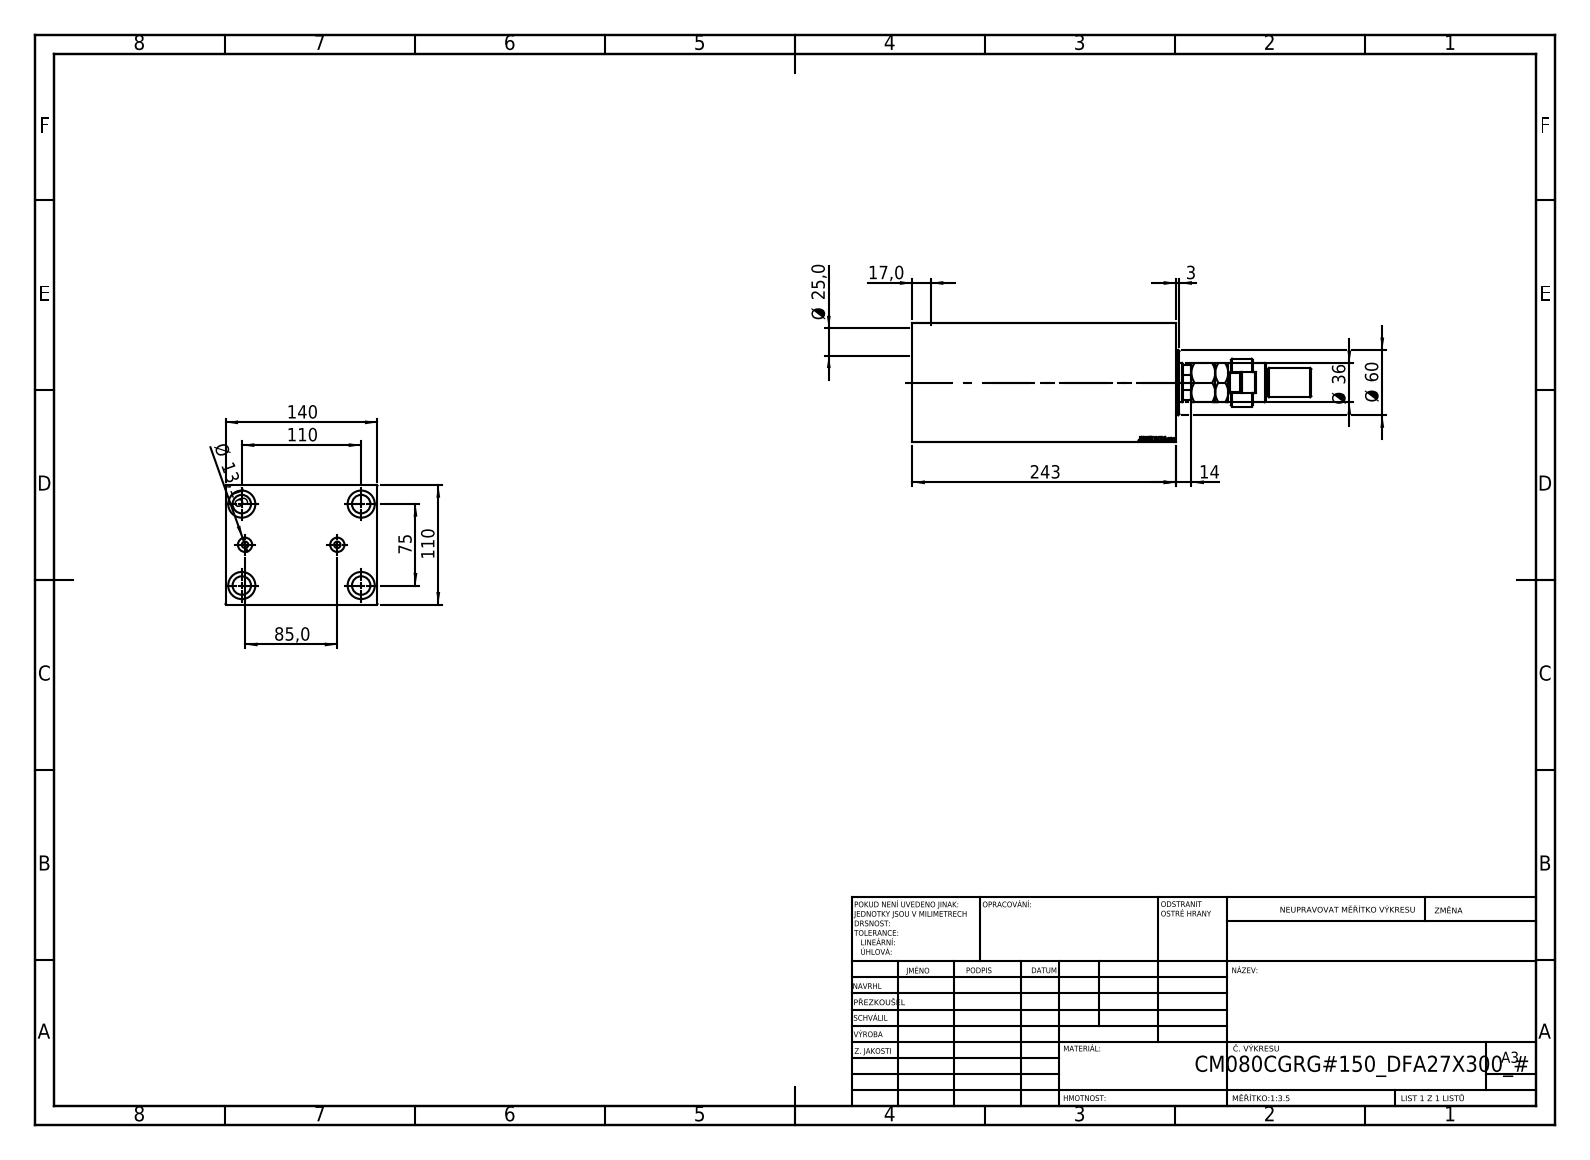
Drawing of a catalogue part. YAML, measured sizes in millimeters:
part_name: "V450CM_VC_B; V450CM_C_VCP; FEMALE_PART_FOR_DFA; V450CM_C_Body (+1 more)"
step_written_by: "SolidWorks 2019 (CONFIG_CONTROL_DESIGN)"
units: millimeters
bodies: {solids: 5, faces: 945, planar: 436, cylindrical: 71, other: 438}
overall_size: [367.5, 140, 110]
volume: 2974000
surface_area: 351122
round_holes:
  - {diameter: 17, count: 4}
  - {diameter: 25, count: 4}
  - {diameter: 6, count: 2}
  - {diameter: 13.16, count: 2}
  - {diameter: 25.5, count: 1}
  - {diameter: 39.5, count: 1}
  - {diameter: 80, count: 1}
  - {diameter: 82, count: 1}
  - {diameter: 87, count: 1}
round_bosses_or_shafts:
  - {diameter: 60, count: 1}
  - {diameter: 44, count: 1}
  - {diameter: 36, count: 1}
  - {diameter: 28, count: 1}
  - {diameter: 27, count: 1}
  - {diameter: 25, count: 1}
  - {diameter: 18, count: 1}
partial_cylinders:
  - {radius: 9.5, count: 1}
  - {radius: 15, count: 1}
  - {radius: 17.5, count: 1}
face_to_face_distances: [110, 140, 243, 222, 21, 14, 229, 208, 164, 150]
hole_center_spacings: [66.57, 37.62, 43.48, 75, 95.66, 110, 113.38, 133.14]
